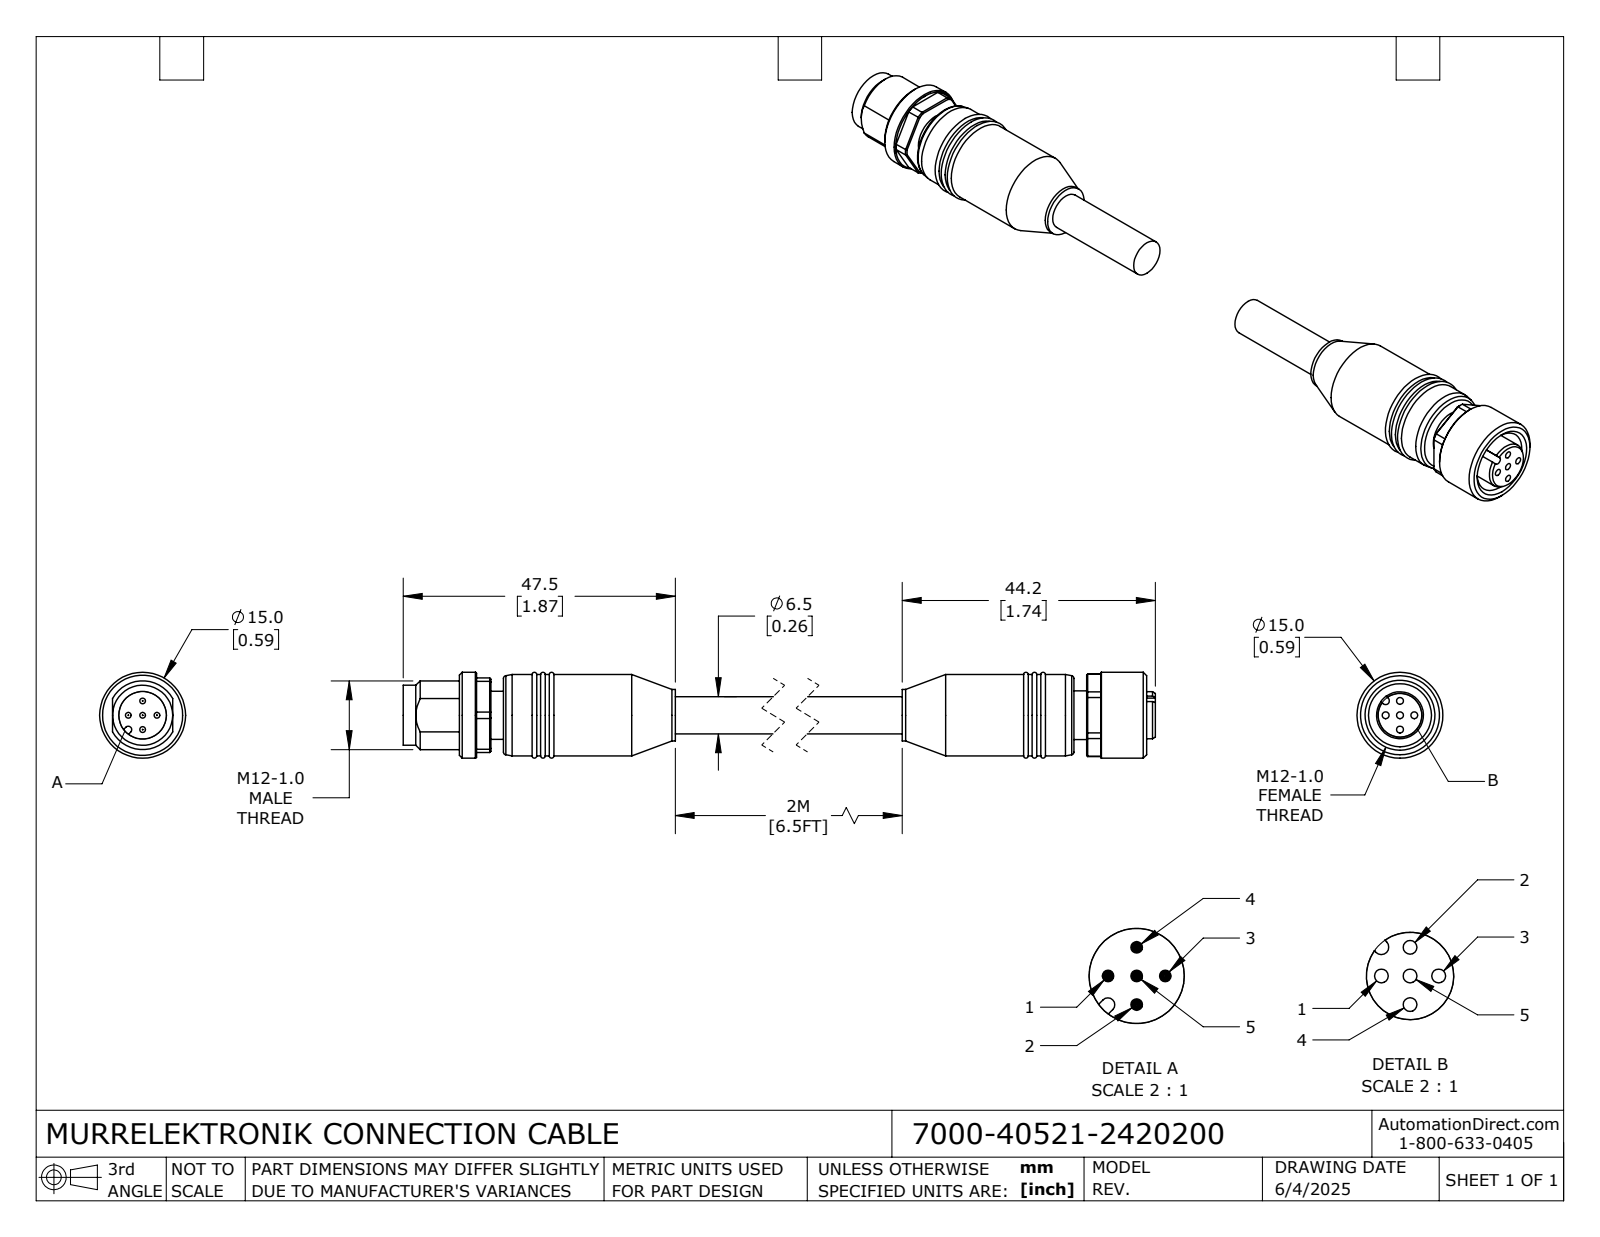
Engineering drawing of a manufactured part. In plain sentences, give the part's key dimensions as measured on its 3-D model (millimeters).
The part is named "7000-40521-2420200_MALE; 7000-40521-2420200; 7000-40521-2420200_FEMALE". Its 3-D file was written by "SolidWorks 2024 (CONFIG_CONTROL_DESIGN)". It is 2 solids with 198 faces: 58 planar, 77 cylindrical and 63 other. Overall it measures 156.7 by 15 by 15 millimeters. Its volume is 13 209 cubic millimeters and its surface area 6 539 square millimeters. Round holes: 5 of diameter 1.2, 1 of diameter 8.3, 1 of diameter 11. Round bosses or shafts: 5 of diameter 1, 1 of diameter 15, 1 of diameter 14.2, 1 of diameter 10.5, 1 of diameter 9, 1 of diameter 8.5, 1 of diameter 8.4, 1 of diameter 8.2. Partial cylindrical surfaces (rounded edges, fillets, slot ends): 1 of radius 0.6, 1 of radius 0.65, 1 of radius 6, 1 of radius 7.2. The main face-to-face distances are 2.2, 127.2, 13, 129.4, 10.5, 125, 134.9, 52.2, 77.2, 50. The hole center spacings are 2.5, 3.54, 5.
